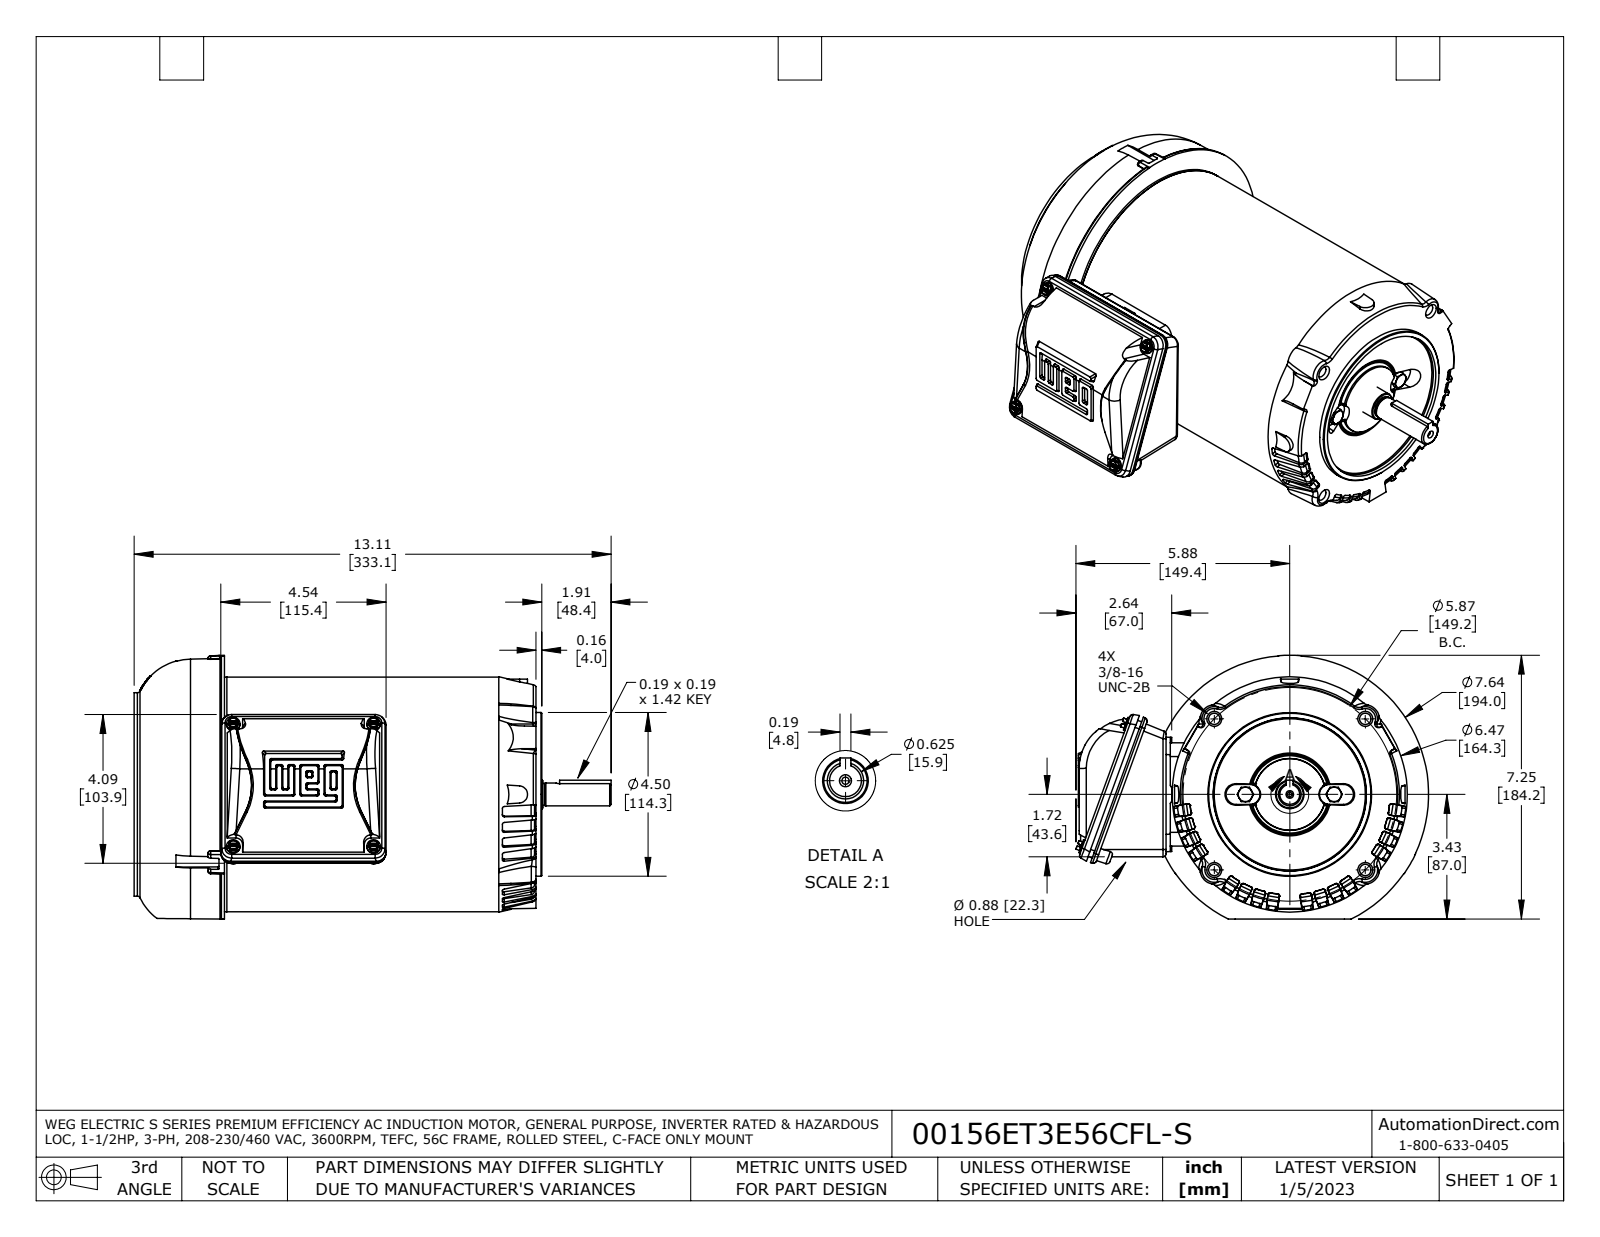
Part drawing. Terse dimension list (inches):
name: 56C_3PH_TEFC_GP_13109 fxt_FL
written by: SolidWorks 2021 (AUTOMOTIVE_DESIGN)
unit: in
bodies: 12 solids, 1274 faces (471 planar, 275 cylindrical, 528 other)
size: 13.114 × 9.7 × 7.551
volume: 407.4 in³; area: 555.9 in²
holes: 4× ⌀0.313, 1× ⌀0.124
bosses: 4× ⌀0.374, 2× ⌀0.35, 1× ⌀6.447, 1× ⌀6.447, 1× ⌀5.591, 1× ⌀4.5, 1× ⌀0.783, 1× ⌀0.625
rounds: 40× R0.047, 38× R0.006, 32× R0.051, 12× R0.059, 12× R0.087, 10× R0.02, 8× R0.205, 8× R0.276
face distances: 7.547, 2.283, 9.831, 10.854, 8.571, 1.024, 0.197, 2.48, 10.028, 11.051
hole spacings: 2.937, 4.154, 5.874
